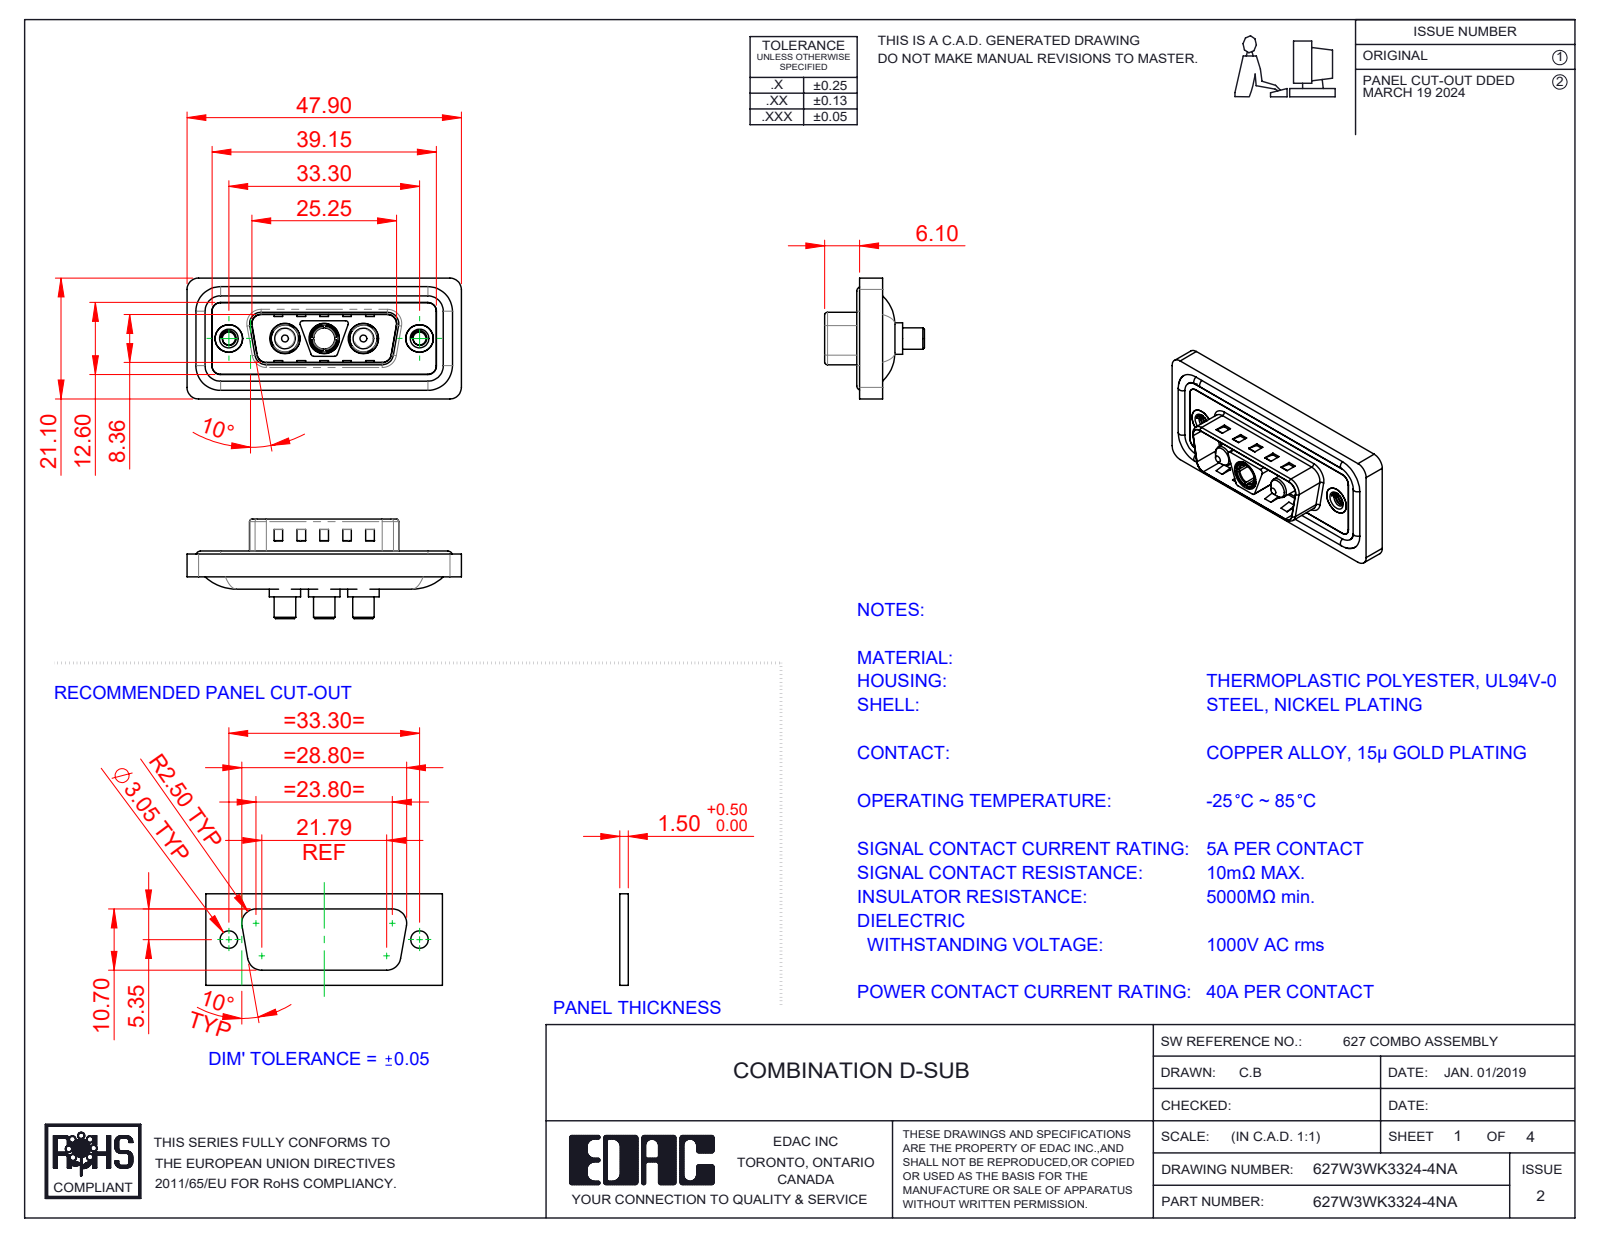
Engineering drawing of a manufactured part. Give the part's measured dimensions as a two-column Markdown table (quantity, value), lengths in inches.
| quantity | value |
| --- | --- |
| part name | 627Combo Waterproof Housing_15 Contacts; 627Combo Shell Front_15 Contacts; 627Combo Threaded Rivet_A; Power Socket_40A S (+4 more) |
| STEP written by | SolidWorks 2023 (CONFIG_CONTROL_DESIGN) |
| units | inches |
| bodies | 13 solids, 607 faces (231 planar, 252 cylindrical, 124 other) |
| overall size | 1.886 × 0.831 × 0.685 |
| volume | 0.351 in³ |
| surface area | 14.19 in² |
| round holes (diameter × count) | 0.191 × 3, 0.209 × 3, 0.089 × 2, 0.157 × 2, 0.189 × 2, 0.197 × 2, 0.146 × 1 |
| round bosses / shafts (diameter × count) | 0.063 × 4, 0.217 × 3, 0.205 × 3, 0.187 × 3, 0.148 × 3, 0.193 × 2, 0.142 × 2, 0.195 × 1 |
| partial cylindrical surfaces (radius × count) | 0.059 × 26, 0.079 × 20, 0.02 × 12, 0.063 × 8, 0.01 × 4, 0.024 × 4, 0.026 × 4, 0.035 × 4 |
| main face-to-face distances | 0.016, 0.043, 0.02, 0.059, 0.063, 0.122, 0.114, 0.157, 0.032, 0.377 |
| hole center spacings | 0.27, 0.386, 0.656, 0.925, 0.539, 1.311 |
